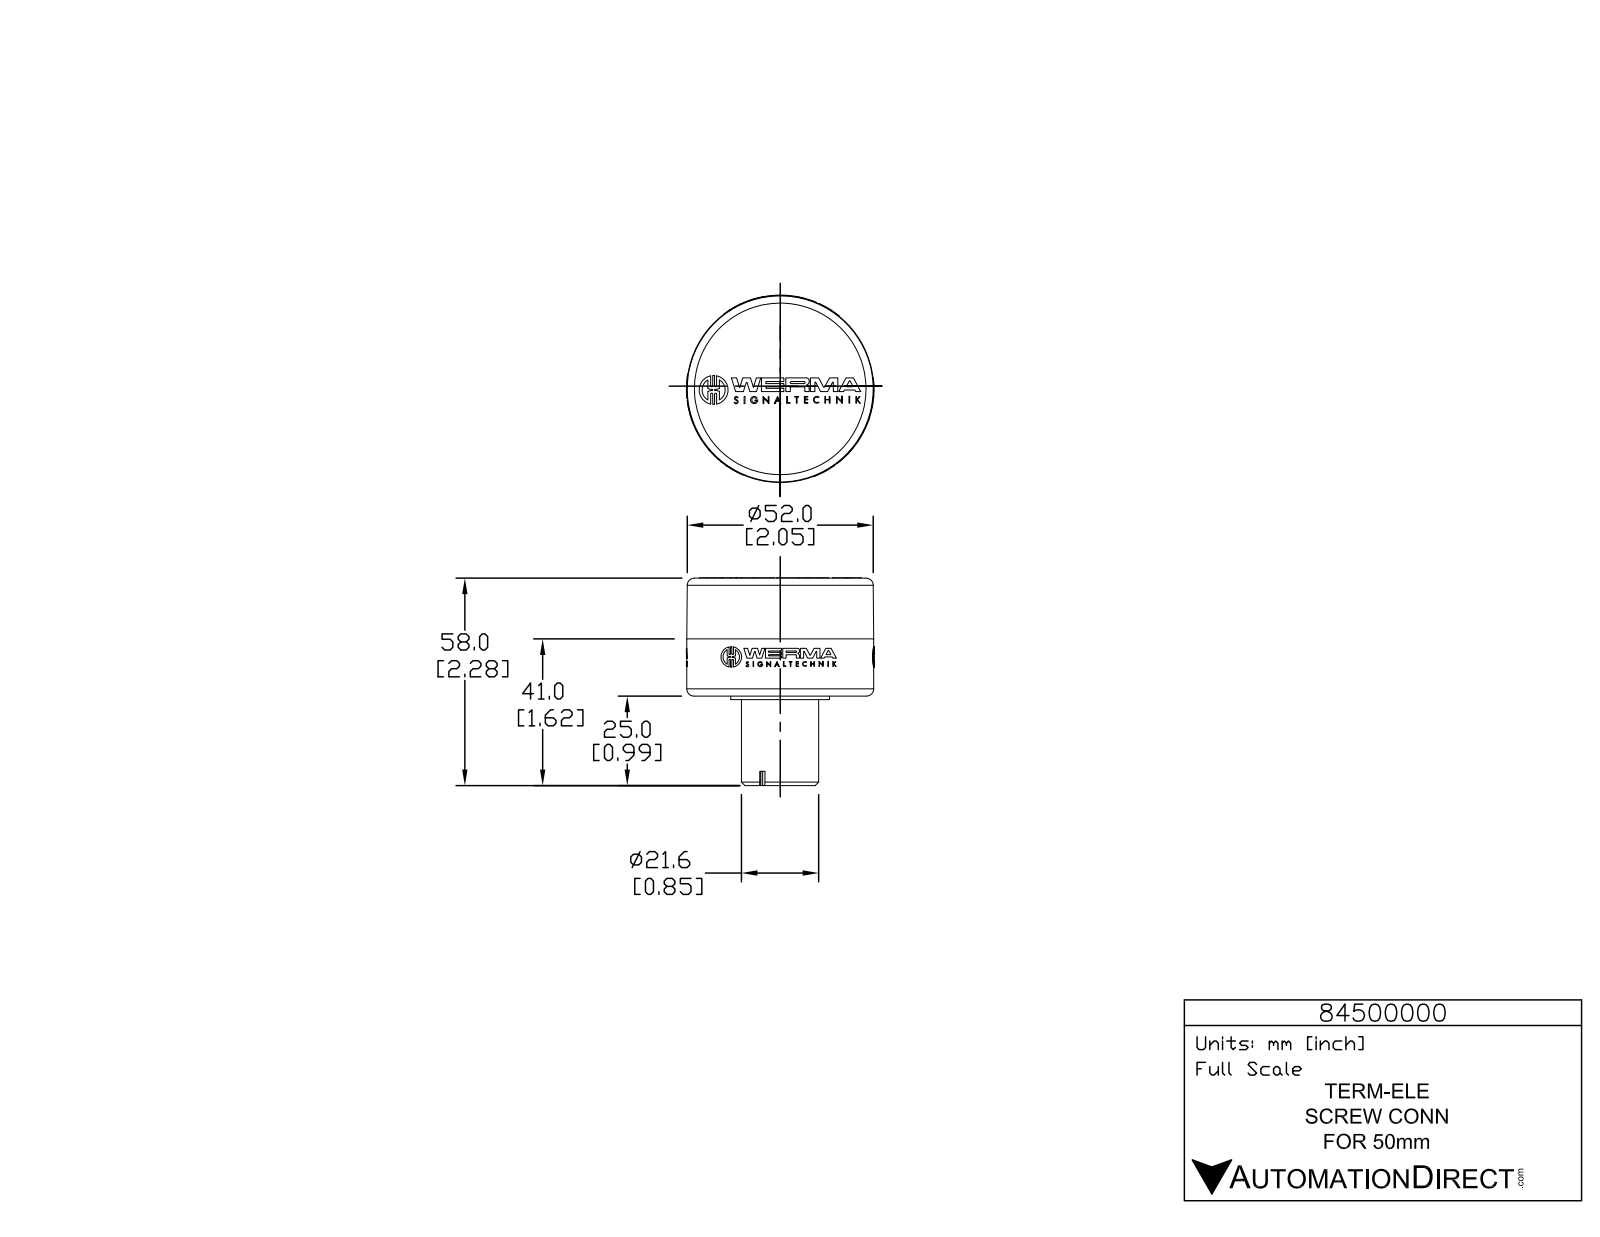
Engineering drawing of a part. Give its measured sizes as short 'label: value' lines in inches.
name: 84500000
written by: SolidWorks 2015 (AUTOMOTIVE_DESIGN)
unit: in
bodies: 2 solids, 1069 faces (740 planar, 317 cylindrical, 12 other)
size: 2.276 × 2.055 × 2.051
volume: 3.29 in³; area: 46.87 in²
holes: 3× ⌀0.039, 1× ⌀0.055, 1× ⌀0.236, 1× ⌀0.433, 1× ⌀1.004, 1× ⌀1.74, 1× ⌀1.772, 1× ⌀1.898
bosses: 3× ⌀0.226, 3× ⌀0.056, 1× ⌀2.047, 1× ⌀1.89, 1× ⌀1.457, 1× ⌀1.083, 1× ⌀0.85, 1× ⌀0.316
rounds: 6× R0.008, 6× R0.008, 6× R0.008, 6× R0.131, 4× R0.014, 3× R0.004, 3× R0.005, 3× R0.005
face distances: 0.197, 0.079, 0.276, 0.039, 0.157, 0.236, 1.287, 1.012, 1.091, 1.248
hole spacings: 0.156, 0.161, 0.227, 0.31, 0.365, 0.526
